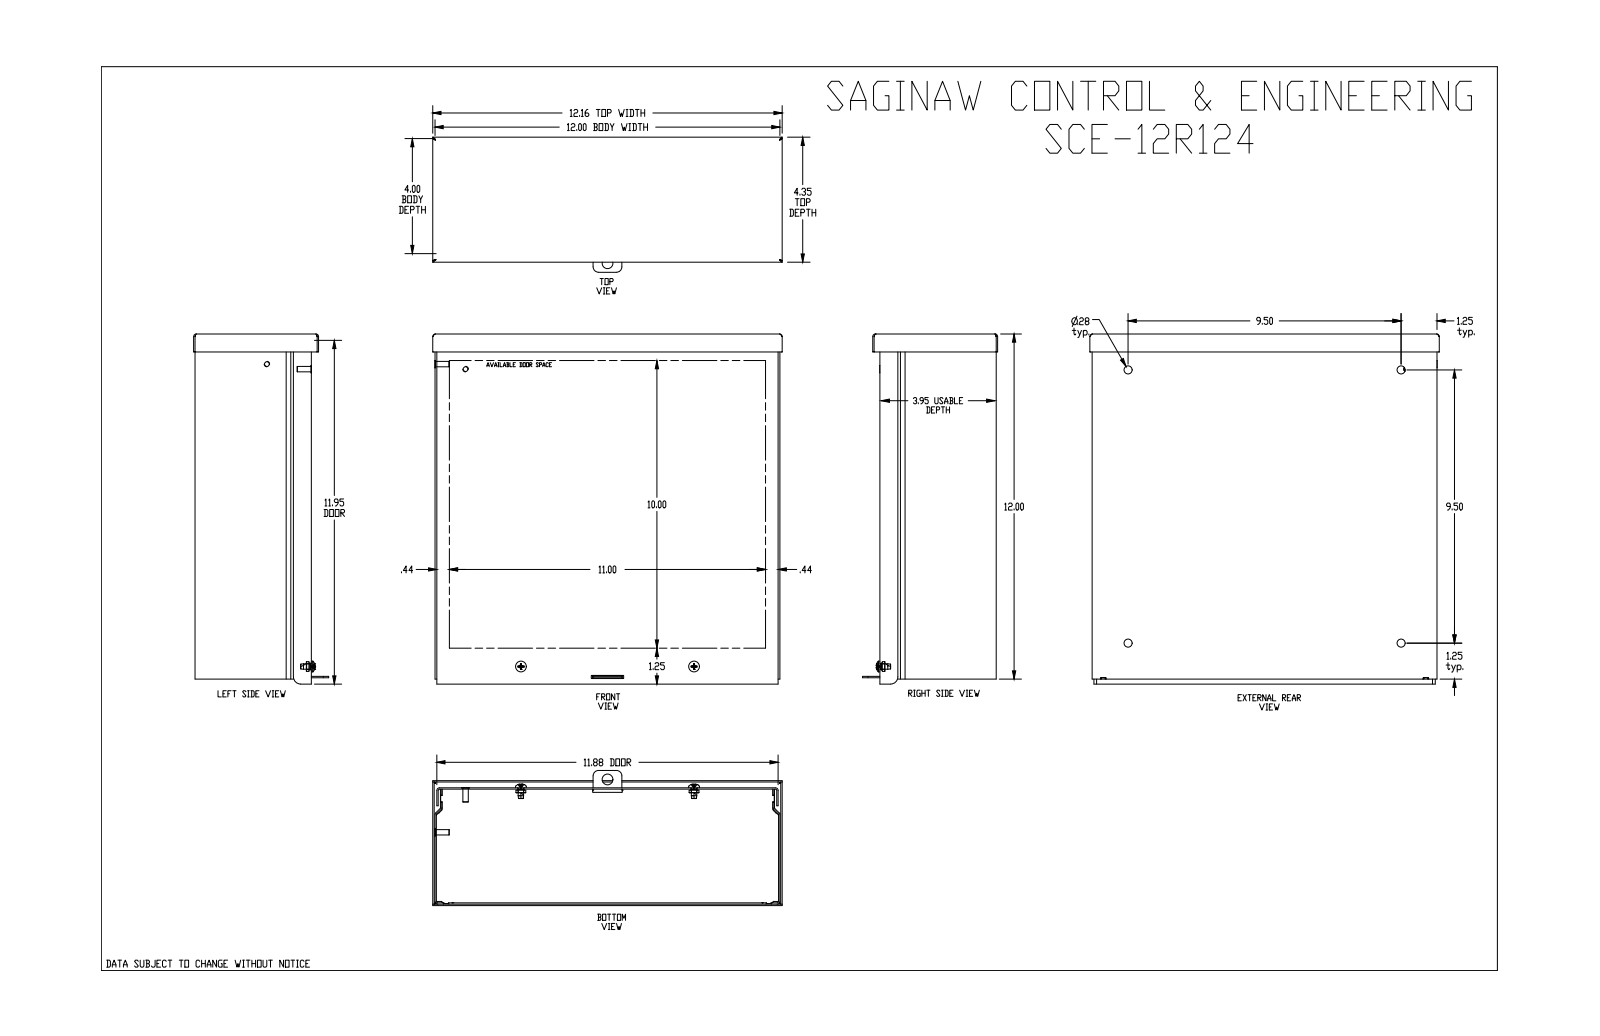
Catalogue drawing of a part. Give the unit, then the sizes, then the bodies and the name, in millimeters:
Units: millimetres
Overall size (bounding box): 309.2 × 308.8 × 119.3
Round holes (diameter × count): ⌀7.1 ×4, ⌀4.8 ×3, ⌀6.4 ×2, ⌀4.8 ×1, ⌀4.9 ×1, ⌀9.5 ×1
Round bosses / shafts (diameter × count): ⌀4.8 ×4, ⌀9.5 ×2, ⌀8.6 ×2, ⌀6.5 ×2, ⌀6.3 ×2
Partial cylindrical surfaces — rounded edges, fillets, slot ends (radius × count): R0.4 ×32, R3.2 ×12, R1.2 ×8, R1.5 ×8, R2.4 ×8, R0.6 ×4, R1.6 ×4, R1.9 ×4
Main face-to-face distances: 1.2, 101.6, 102.8, 100.4, 303.6, 304.8, 1.5, 302.4, 302.1, 303.3
Hole centre spacings: 241.3, 48.7, 198.2, 265.6, 327.8, 341.2, 4.8, 33.9
Volume: 437 700 mm³ · Surface area: 701 300 mm²
Bodies: 11 solids, 398 faces (181 planar, 143 cylindrical, 74 other)
Part name (STEP PRODUCT): SCE-12R124
STEP written by: SolidWorks 2019 (AUTOMOTIVE_DESIGN)
